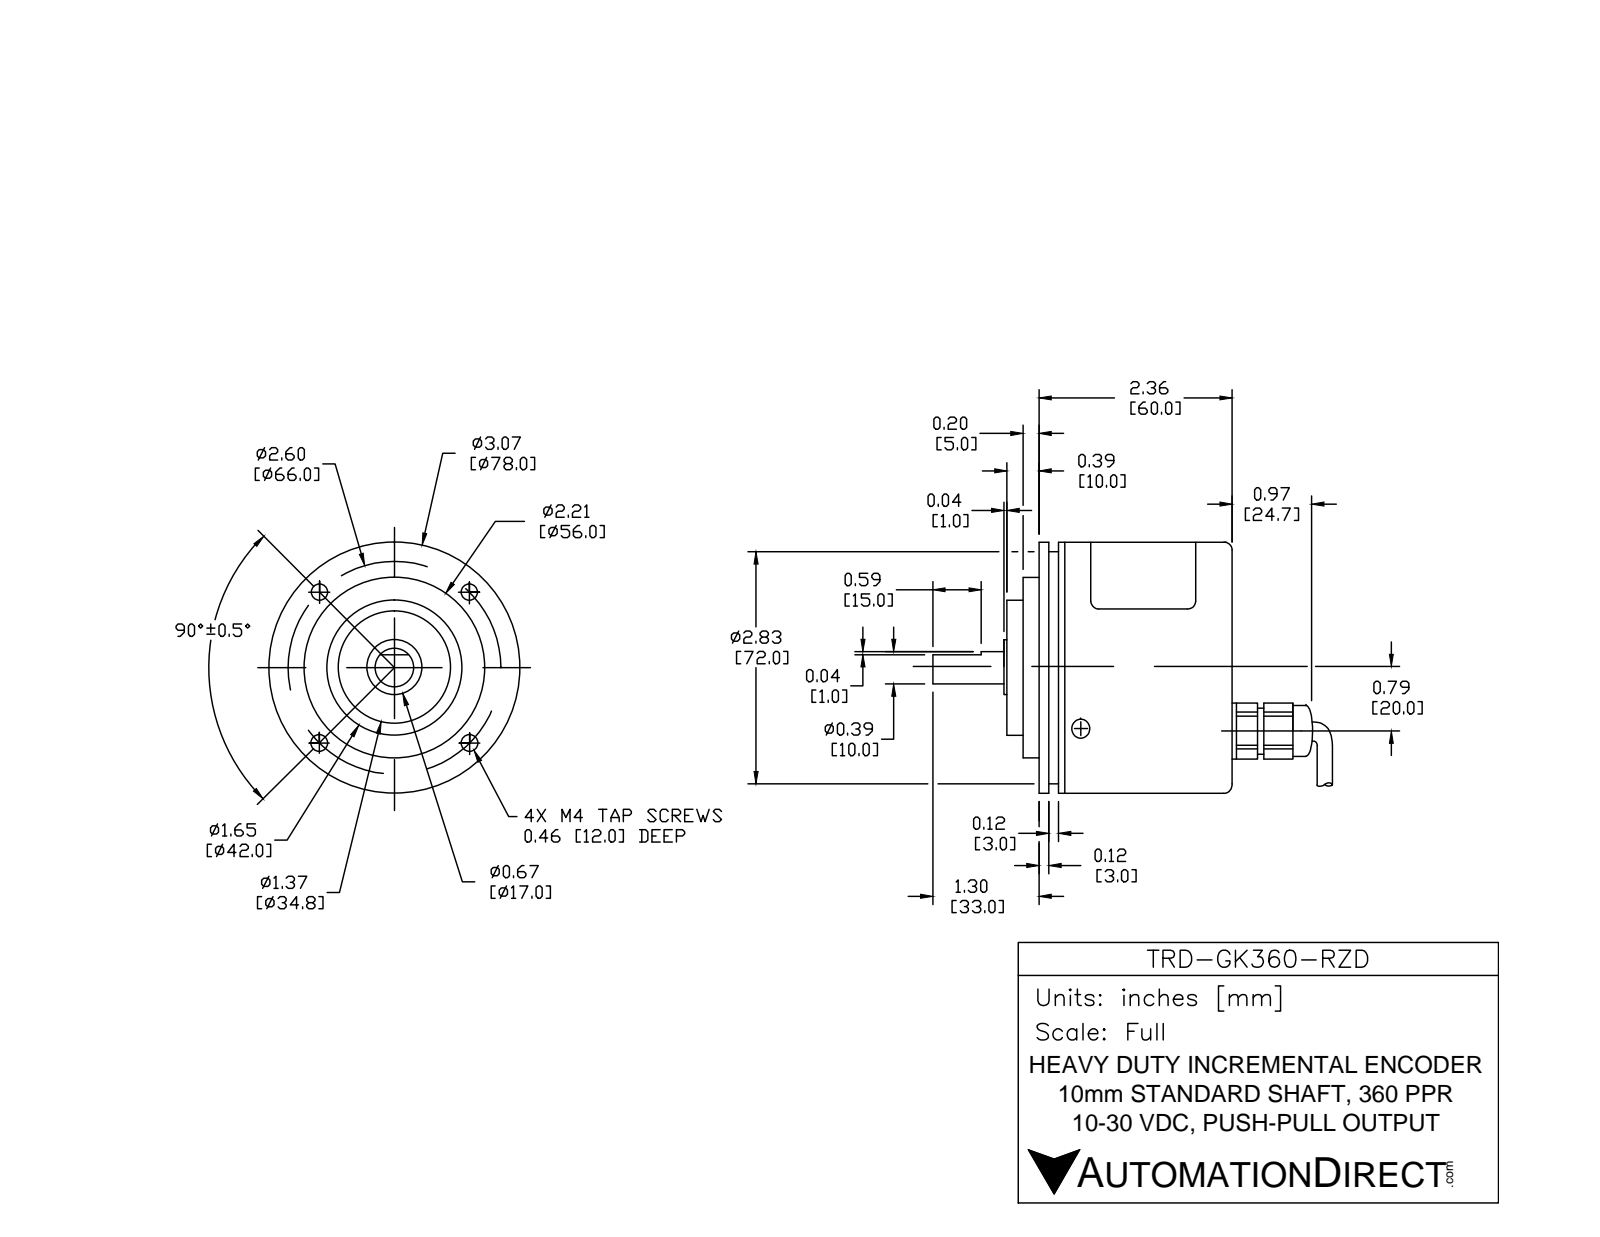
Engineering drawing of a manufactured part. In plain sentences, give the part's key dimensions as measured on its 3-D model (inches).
The part is named "TRD-GK". Its 3-D file was written by "SolidWorks 2016 (AUTOMOTIVE_DESIGN)". It is 1 solid with 144 faces: 48 planar, 55 cylindrical and 41 other. Overall it measures 5.157 by 4.291 by 3.071 inches. Its volume is 18.91 cubic inches and its surface area 48.07 square inches. Round holes: 4 of diameter 0.13, 2 of diameter 0.169, 1 of diameter 0.276. Round bosses or shafts: 3 of diameter 0.205, 2 of diameter 0.236, 1 of diameter 3.071, 1 of diameter 2.835, 1 of diameter 2.205, 1 of diameter 1.654, 1 of diameter 1.378, 1 of diameter 0.669. Partial cylindrical surfaces (rounded edges, fillets, slot ends): 1 of radius 1.5. The main face-to-face distances are 2.362, 0.118, 0.197, 2.559, 0.315, 0.236, 2.126, 2.244, 0.433, 0.65. The hole center spacings are 1.837, 0.928, 1.937, 2.598.
